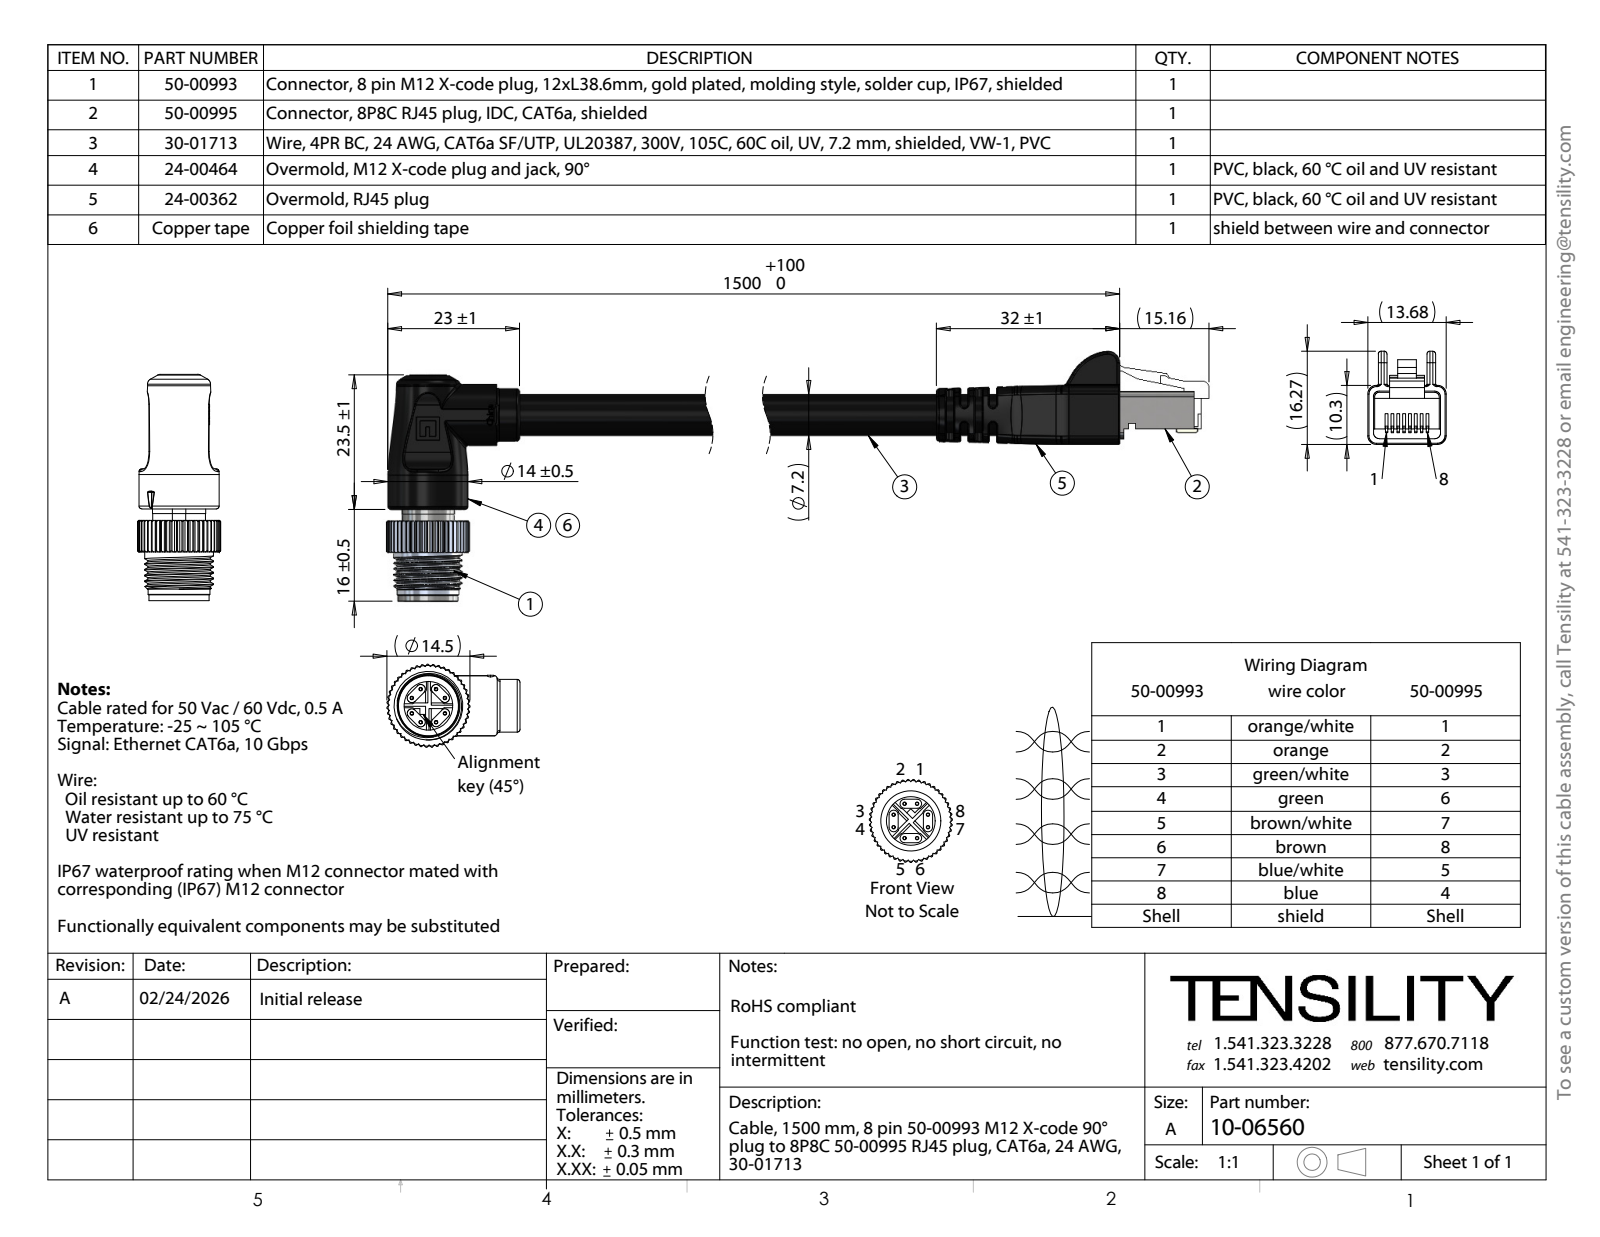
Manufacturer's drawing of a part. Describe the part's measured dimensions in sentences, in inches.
The part is named "50-00995; 24-00464; 50-00993-03; 50-00993-04_默认 (+7 more)". Its 3-D file was written by "SolidWorks 2025 (CONFIG_CONTROL_DESIGN)". It is 95 solids with 2077 faces: 843 planar, 677 cylindrical and 557 other. Overall it measures 8.281 by 1.717 by 0.57 inches. Its volume is 0.956 cubic inches and its surface area 76.88 square inches. Round holes: 56 of diameter 0.008, 8 of diameter 0.024, 8 of diameter 0.047, 1 of diameter 0.079, 1 of diameter 0.098, 1 of diameter 0.198, 1 of diameter 0.207, 1 of diameter 0.222, 1 of diameter 0.226, 1 of diameter 0.295, 1 of diameter 0.335, 1 of diameter 0.357. Round bosses or shafts: 8 of diameter 0.055, 8 of diameter 0.045, 8 of diameter 0.041, 8 of diameter 0.031, 2 of diameter 0.362, 1 of diameter 0.551, 1 of diameter 0.472, 1 of diameter 0.433. Partial cylindrical surfaces (rounded edges, fillets, slot ends): 14 of radius 0.02, 13 of radius 0.039, 12 of radius 0.004, 11 of radius 0.008, 10 of radius 0.031, 8 of radius 0.024, 8 of radius 0.059, 4 of radius 0.085. The main face-to-face distances are 0.02, 0.039, 0.039, 0.039, 0.079, 0.049, 0.197, 0.154, 0.148, 0.106. The hole center spacings are 0.014, 0.063, 0.07, 0.126, 0.016, 0.042, 0.056, 0.076.
